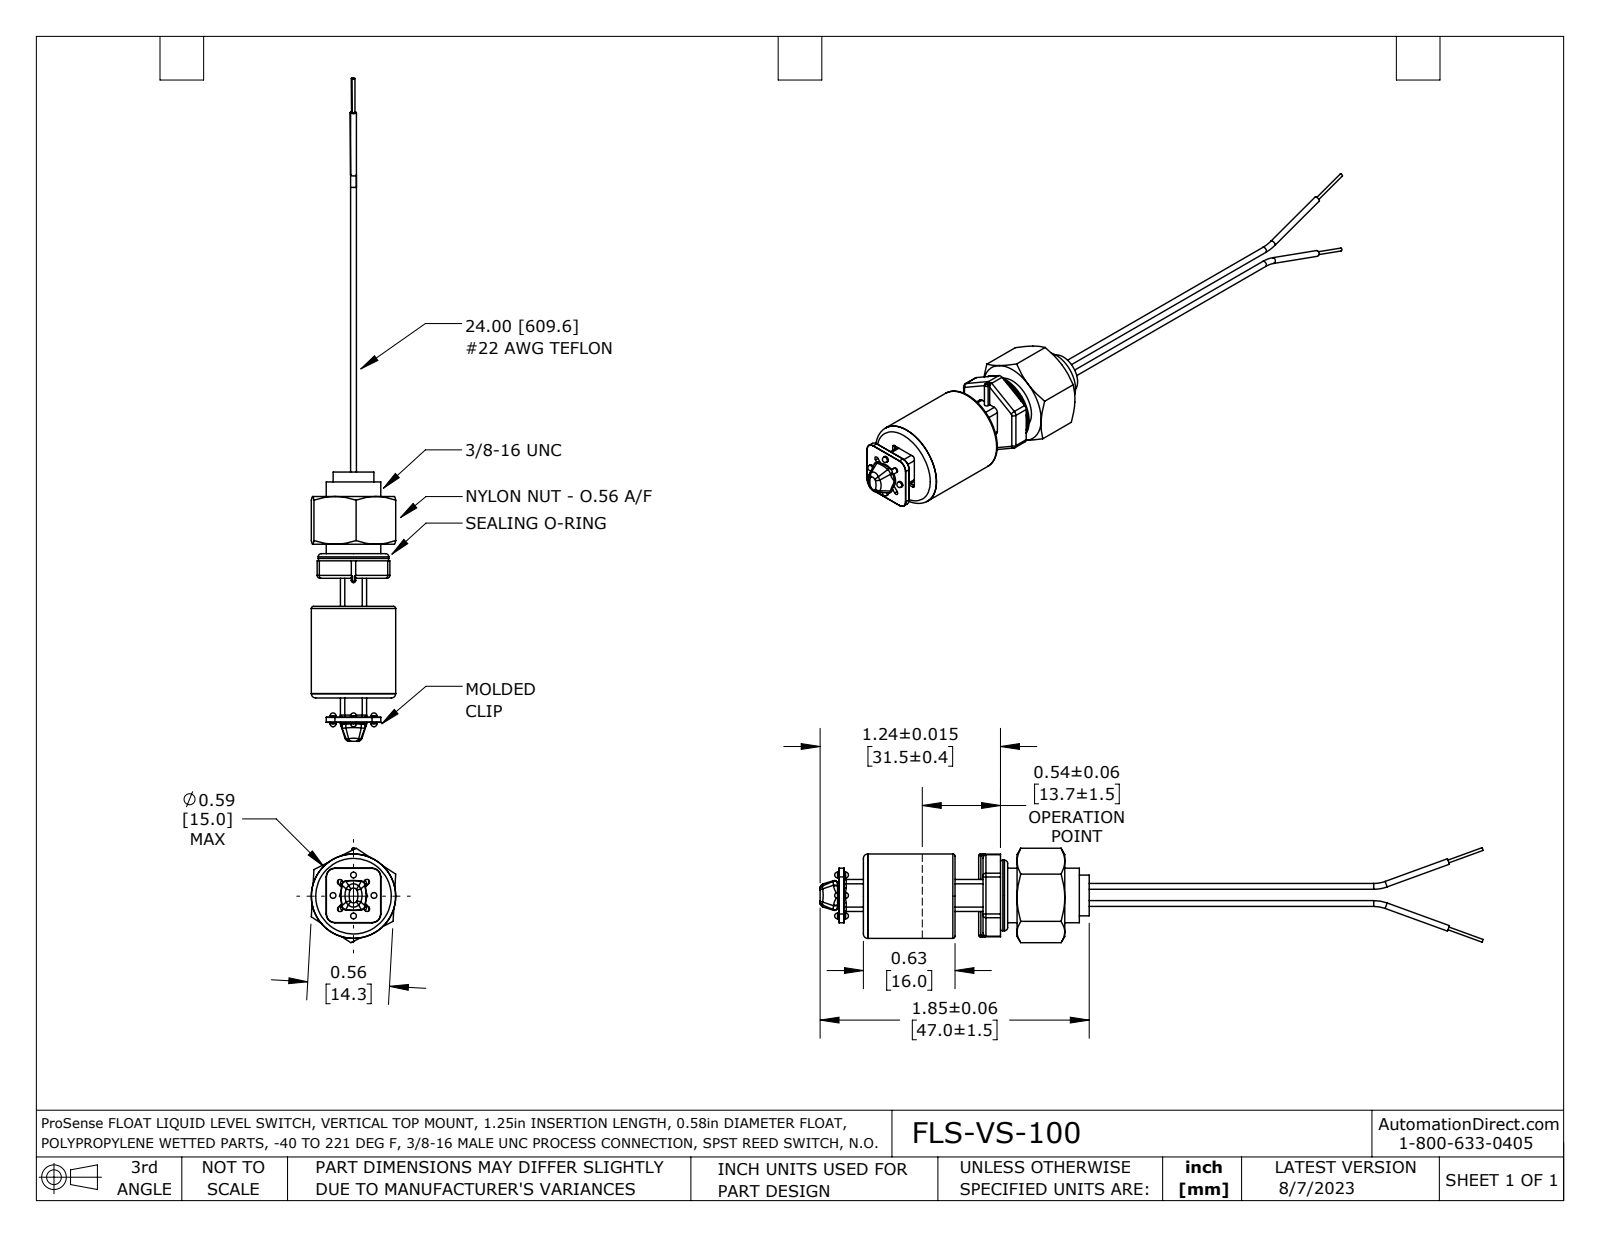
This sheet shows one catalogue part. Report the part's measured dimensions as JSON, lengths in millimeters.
{"part_name": "ADM3326-NO r1 nc fxt", "step_written_by": "SolidWorks 2021 (AUTOMOTIVE_DESIGN)", "units": "millimeters", "bodies": {"solids": 12, "faces": 431, "planar": 139, "cylindrical": 159, "other": 133}, "overall_size": [115.8, 16.6, 14.7], "volume_mm3": 4200, "surface_area_mm2": 6858, "round_holes": [[1.7, 2], [0.7, 1], [0.7, 1], [4.6, 1], [4.7, 1], [7.8, 1], [9.5, 1], [12.6, 1], [12.7, 1], [14.2, 1]], "round_bosses_or_shafts": [[1, 8], [1.6, 2], [1.3, 2], [0.5, 2], [14.7, 1], [13.2, 1], [12.3, 1], [7.1, 1]], "partial_cylinders_radius": [[0.3, 15], [0.8, 10], [0.4, 9], [0.5, 6], [0.4, 4], [0.6, 4], [1.1, 4], [1.4, 4]], "face_to_face_distances": [1, 0.8, 6, 14.3, 0.4, 5, 1.4, 6.4, 2.4, 5], "hole_center_spacings": [5.1, 1.3, 1.4, 1.6, 1.7, 3, 3.4, 3.9]}
